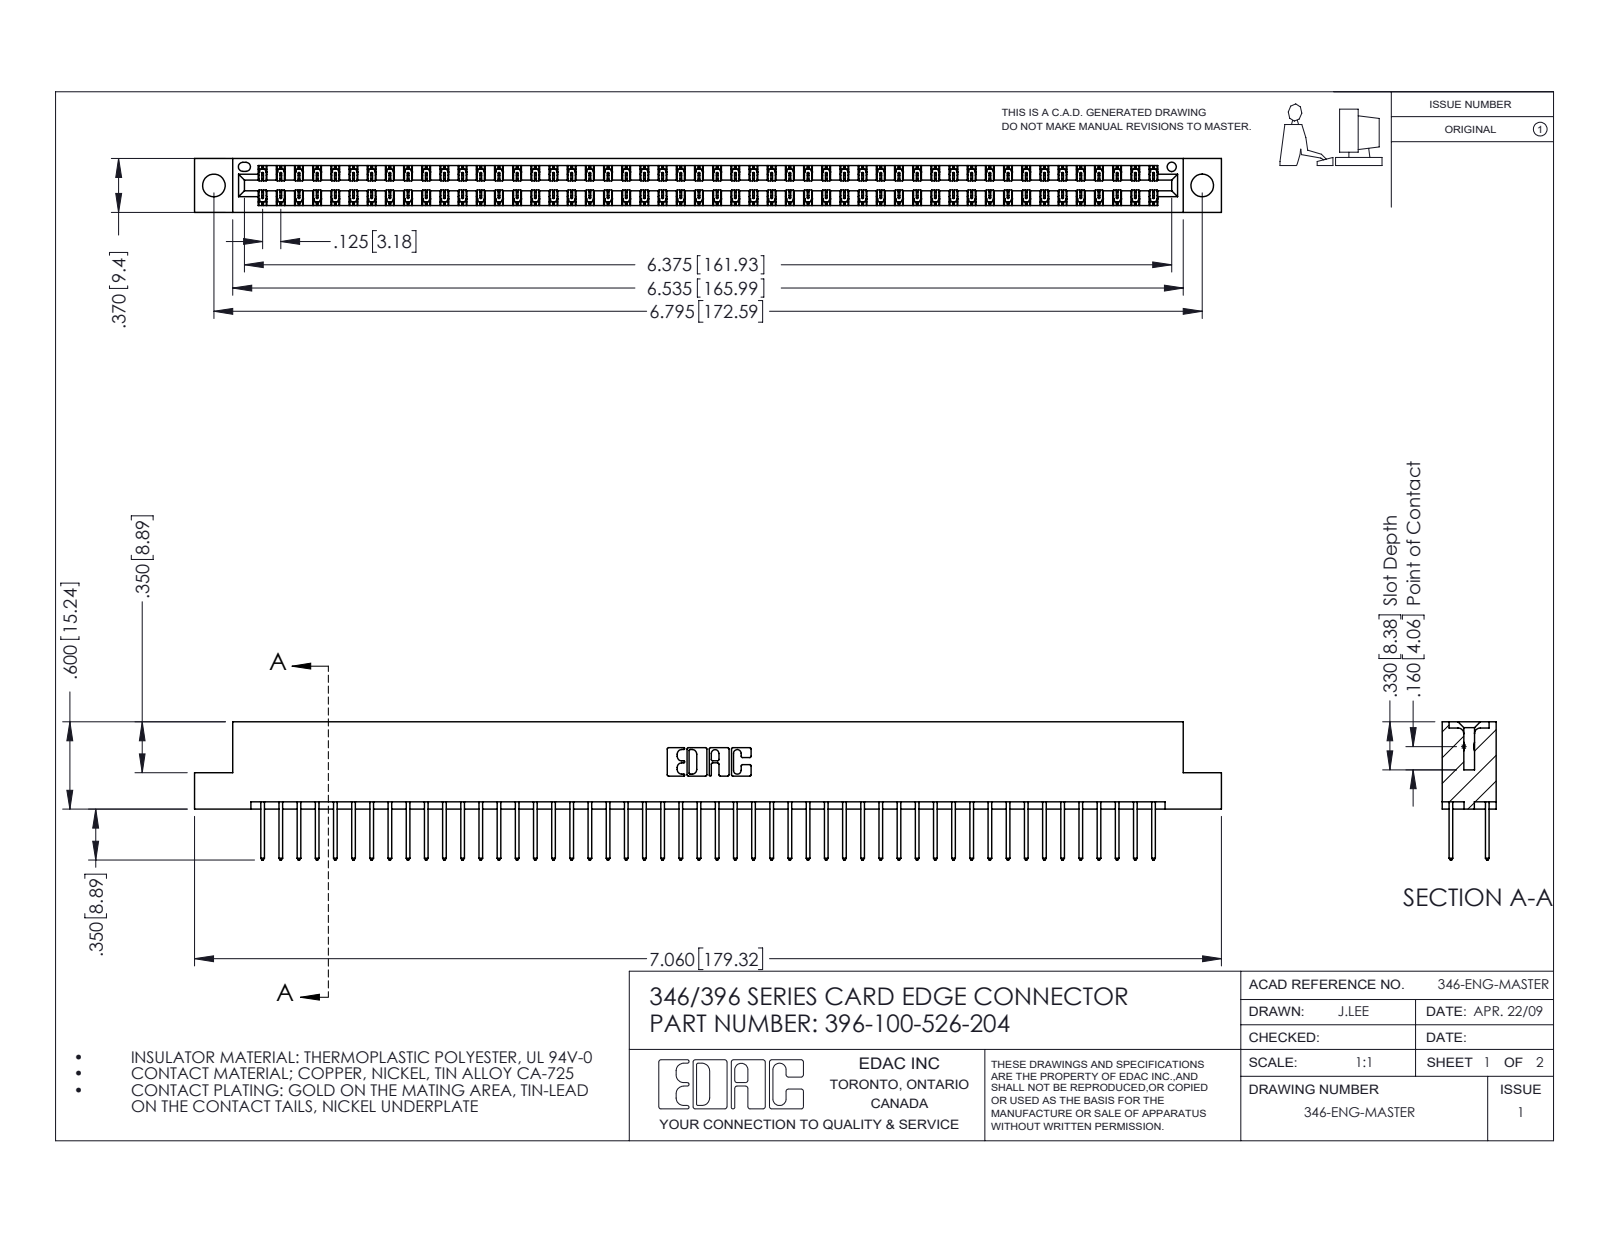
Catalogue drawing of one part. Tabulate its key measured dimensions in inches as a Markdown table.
| quantity | value |
| --- | --- |
| part name | 345-292-001_345-293-126; 346 Part_Flush Mounting Lugs - 0.156 Dia-TH; 396-100-526-204 |
| STEP written by | SolidWorks 2016 (CONFIG_CONTROL_DESIGN) |
| units | inches |
| bodies | 101 solids, 5322 faces (3576 planar, 1746 cylindrical, 0 other) |
| overall size | 7.06 × 0.95 × 0.37 |
| volume | 1.076 in³ |
| surface area | 38.59 in² |
| round holes (diameter × count) | 0.156 × 2, 0.064 × 1 |
| partial cylindrical surfaces (radius × count) | 0.006 × 150, 0.01 × 100, 0.01 × 22, 0.007 × 6, 0.031 × 6, 0.026 × 3, 0.014 × 2, 0.022 × 2 |
| main face-to-face distances | 0.048, 0.322, 0.25, 0.37, 0.072, 0.298, 0.025, 0.275, 0.148, 0.222 |
| hole center spacings | 0.246, 6.586, 6.795 |
